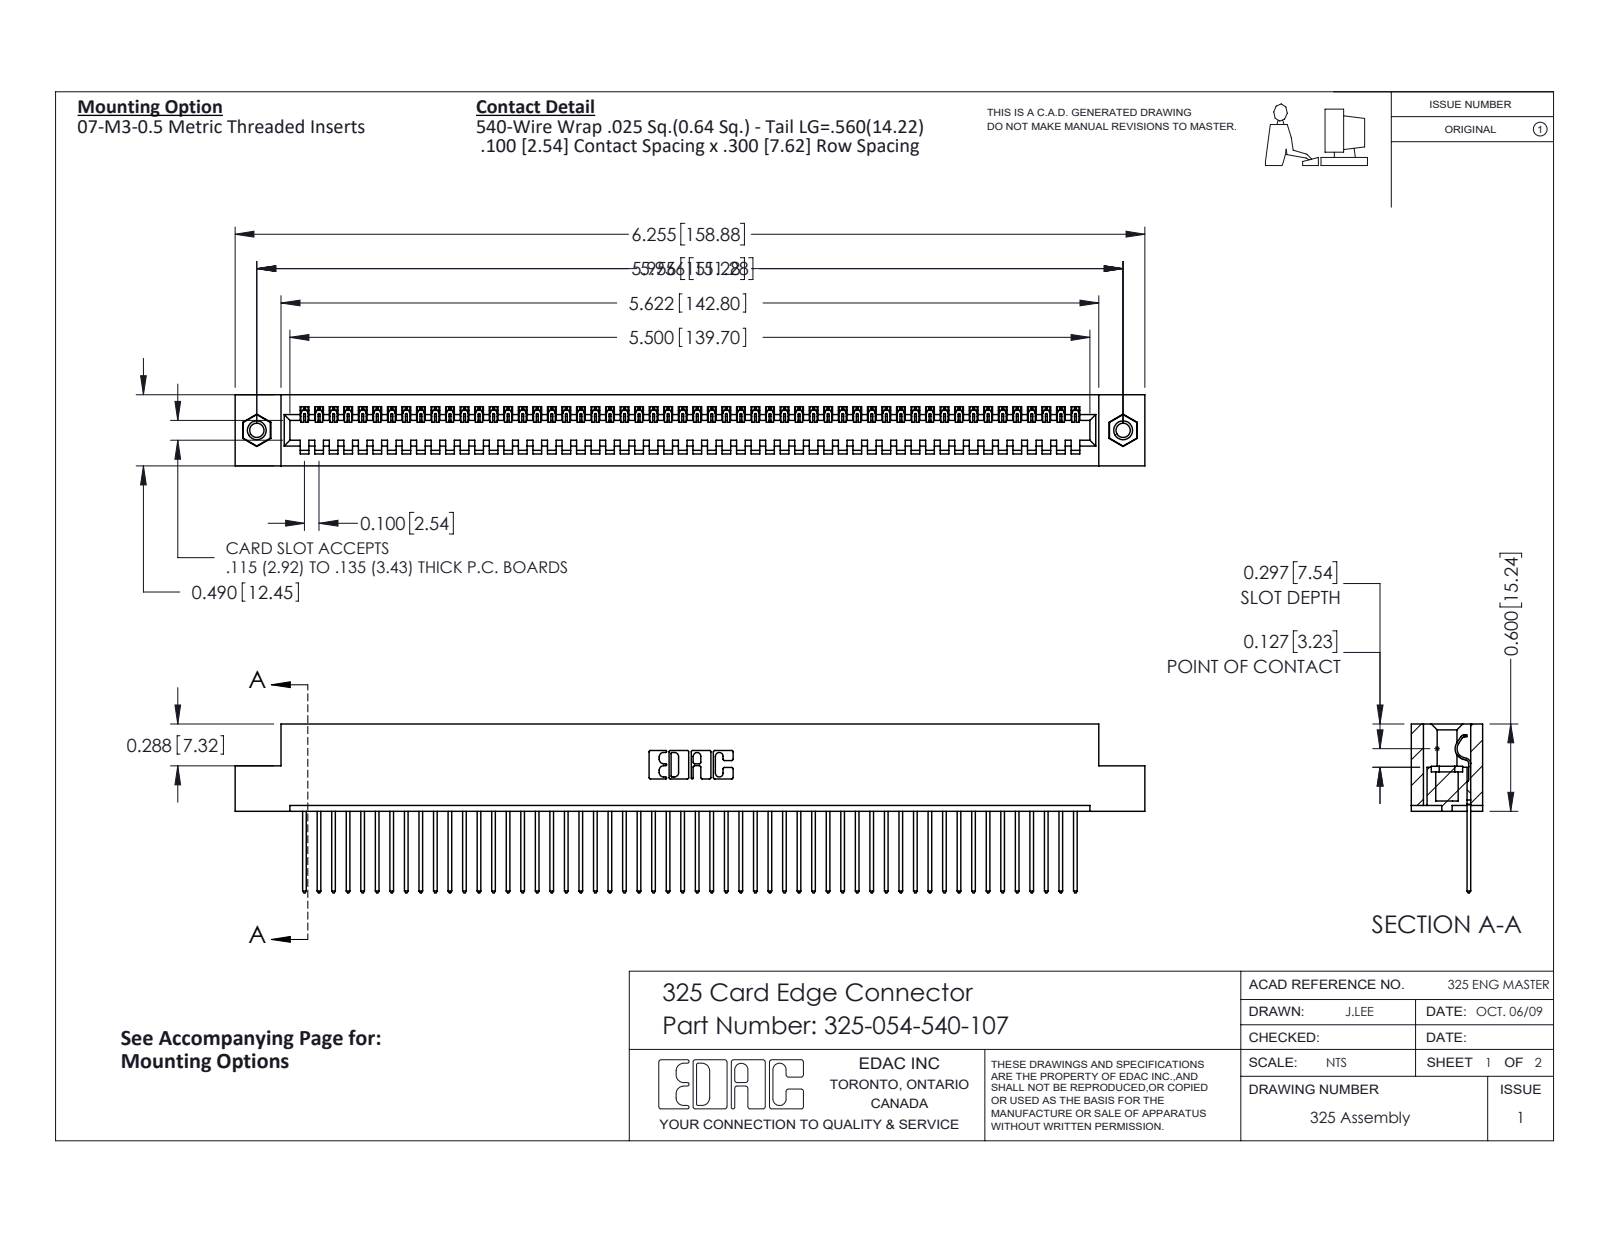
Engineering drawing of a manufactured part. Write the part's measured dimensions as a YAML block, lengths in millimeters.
part_name: "325 Part_TI; 325-054-540-107; 325-292-001_325-293-140; 345-250-001_345-250-005-103"
step_written_by: "SolidWorks 2016 (CONFIG_CONTROL_DESIGN)"
units: millimeters
bodies: {solids: 57, faces: 3306, planar: 2370, cylindrical: 920, other: 16}
overall_size: [158.9, 29.5, 12.4]
volume: 20320
surface_area: 22970
round_holes:
  - {diameter: 2.5, count: 2}
  - {diameter: 3.2, count: 2}
  - {diameter: 4.1, count: 2}
round_bosses_or_shafts:
  - {diameter: 3.9, count: 2}
partial_cylinders:
  - {radius: 0.2, count: 108}
  - {radius: 0.3, count: 108}
  - {radius: 0.3, count: 22}
  - {radius: 0.2, count: 6}
  - {radius: 0.8, count: 6}
  - {radius: 0.7, count: 3}
  - {radius: 0.4, count: 1}
  - {radius: 0.6, count: 1}
face_to_face_distances: [2.1, 10.3, 7.6, 12.4, 2.7, 9.7, 0.6, 8.3, 14.2, 6.7]
hole_center_spacings: [151.3]
